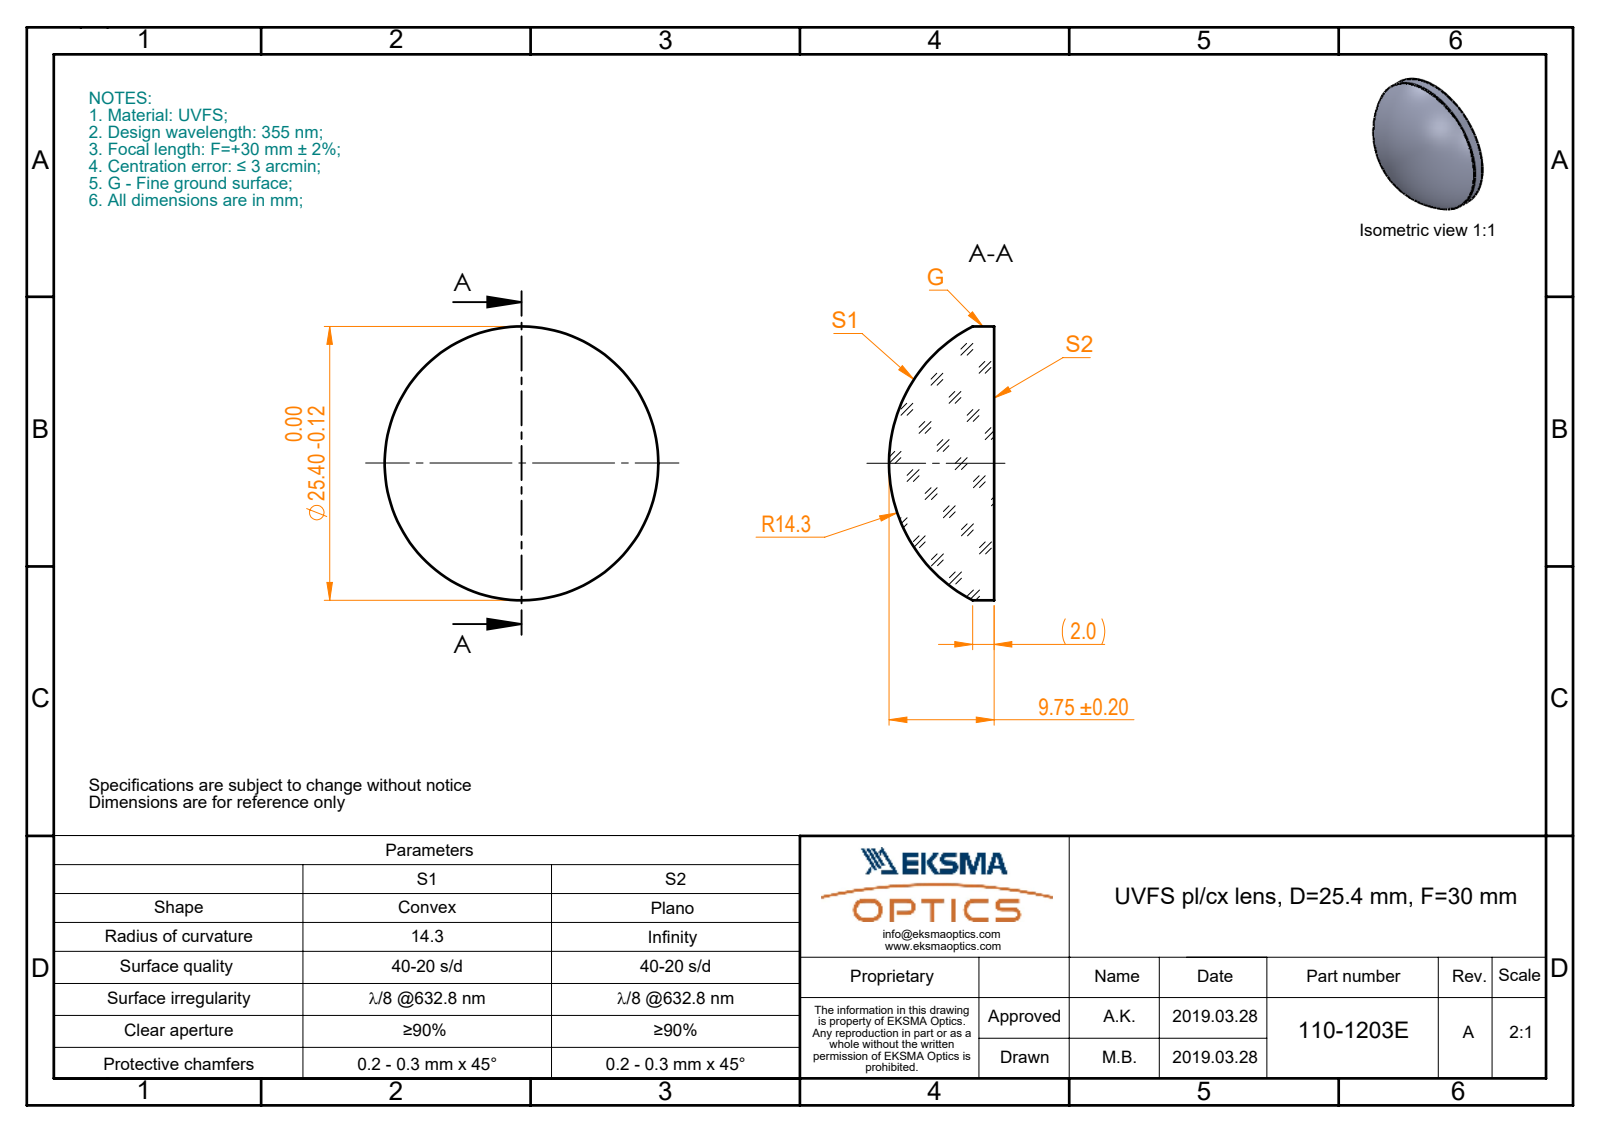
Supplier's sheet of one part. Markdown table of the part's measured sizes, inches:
| quantity | value |
| --- | --- |
| part name | 110-1203E UVFS pl-cx 25.4 F30 |
| STEP written by | SolidWorks 2017 (CONFIG_CONTROL_DESIGN) |
| units | inches |
| bodies | 1 solid, 5 faces (1 planar, 2 cylindrical, 2 other) |
| overall size | 1 × 1 × 0.384 |
| volume | 0.196 in³ |
| surface area | 2.111 in² |
| round bosses / shafts (diameter × count) | 1 × 1 |
